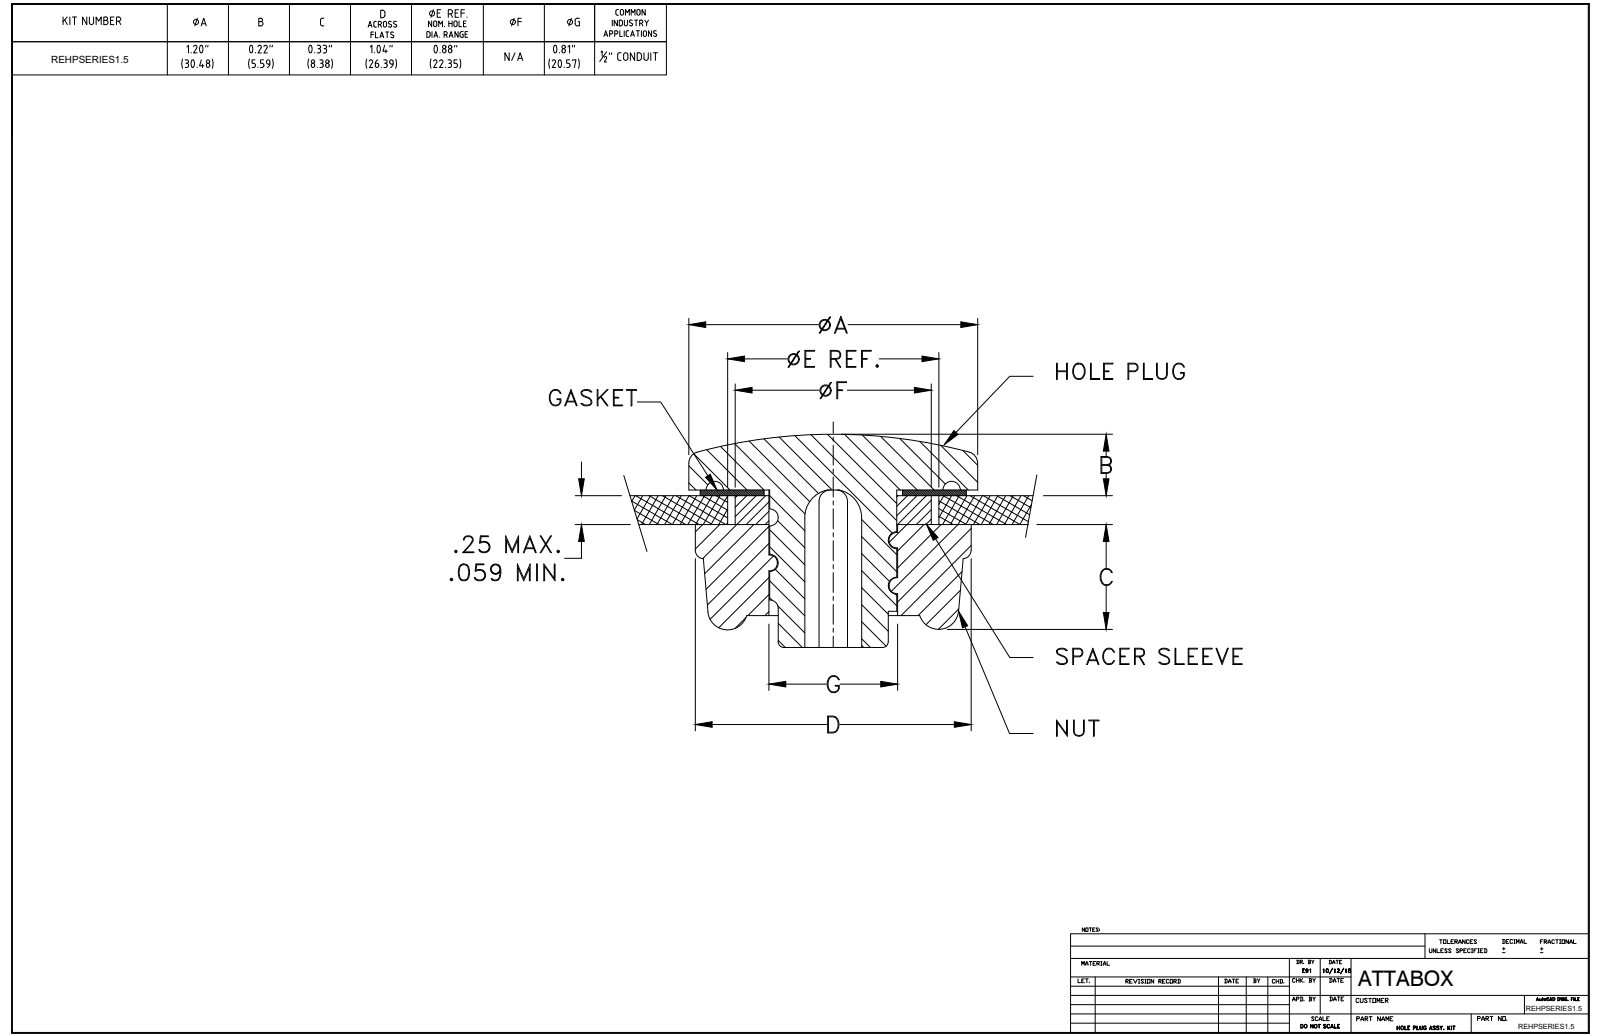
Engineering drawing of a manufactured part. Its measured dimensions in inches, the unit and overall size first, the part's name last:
Units: inches
Overall size (bounding box): 1.2 × 1.2 × 0.734
Round holes (diameter × count): ⌀0.812 ×1, ⌀0.82 ×1
Round bosses / shafts (diameter × count): ⌀1.2 ×1, ⌀0.752 ×1
Partial cylindrical surfaces — rounded edges, fillets, slot ends (radius × count): R0.03 ×8, R0.08 ×8, R0.196 ×6, R0.042 ×2, R0.02 ×1
Main face-to-face distances: 0.089, 0.125, 0.214, 0.31, 0.316, 0.441, 0.53, 0.435, 0.524, 0.196
Volume: 0.543 in³ · Surface area: 9.073 in²
Bodies: 3 solids, 120 faces (35 planar, 47 cylindrical, 38 other)
Part name (STEP PRODUCT): HPSERIES1.5
STEP written by: SolidWorks 2018 (AUTOMOTIVE_DESIGN)
